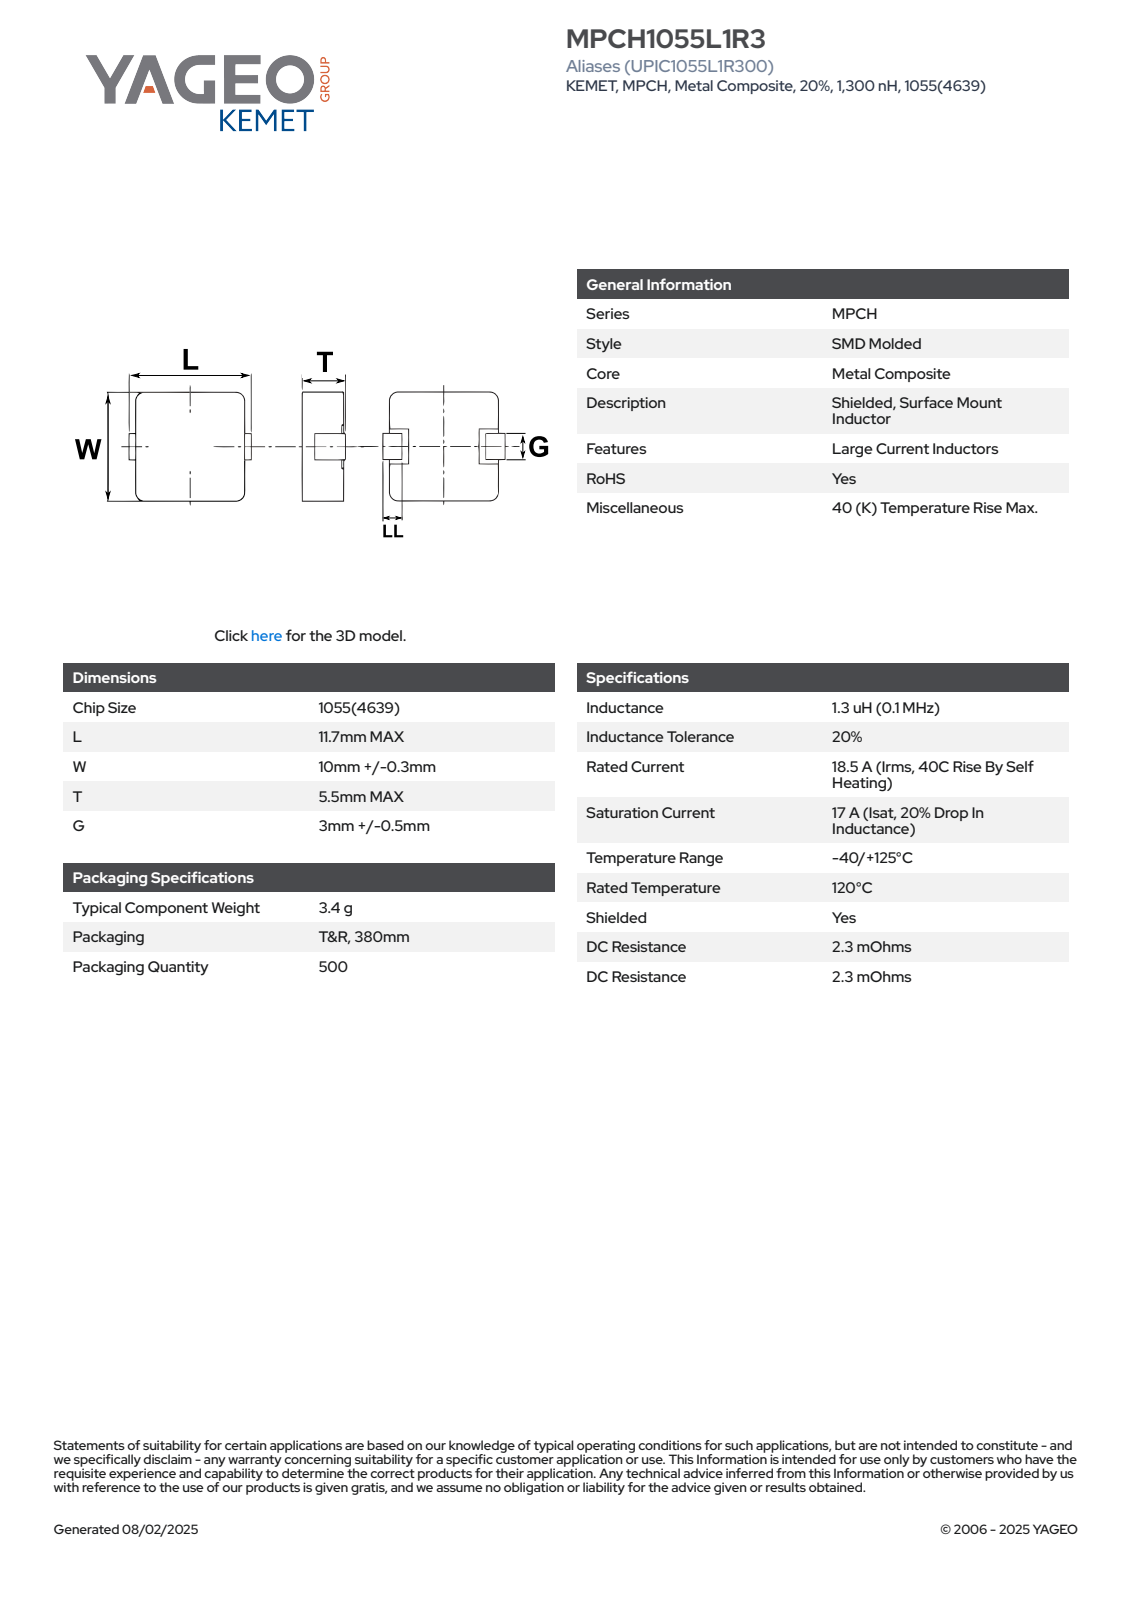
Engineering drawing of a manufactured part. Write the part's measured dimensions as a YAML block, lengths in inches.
part_name: "IS_MPC_4639_L11.7W10.3T5.5LL2.1G3.5"
step_written_by: "SolidWorks 2014 (AUTOMOTIVE_DESIGN)"
units: inches
bodies: {solids: 4, faces: 105, planar: 93, cylindrical: 12, other: 0}
overall_size: [0.461, 0.406, 0.217]
volume: 0.039
surface_area: 0.814
partial_cylinders:
  - {radius: 0.035, count: 4}
face_to_face_distances: [0.215, 0.406, 0.444, 0.453, 0.445, 0.452, 0.444, 0.457, 0.448, 0.449]
